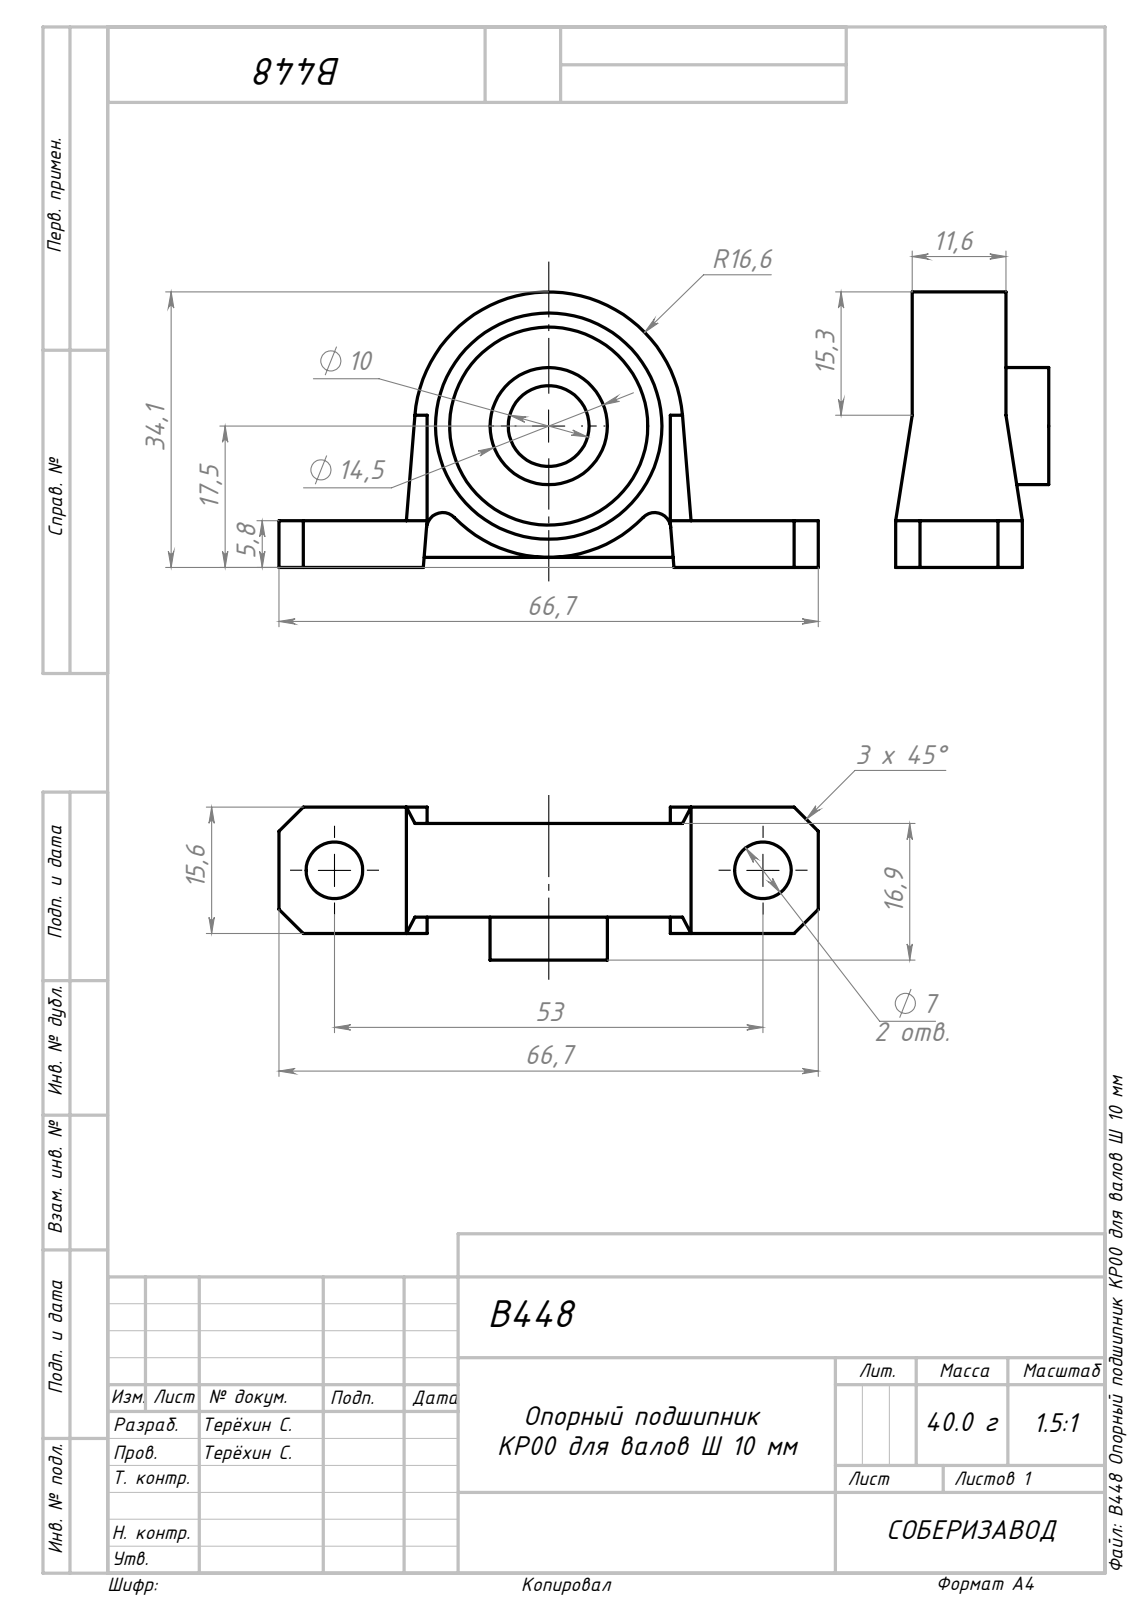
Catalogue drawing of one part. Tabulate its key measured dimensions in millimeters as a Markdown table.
| quantity | value |
| --- | --- |
| part name | B448 Опорный подшипник KP00 для валов Ø 10 мм_00; Сборка2 |
| STEP written by | SolidWorks 2024 (AUTOMOTIVE_DESIGN) |
| units | millimeters |
| bodies | 3 solids, 64 faces (39 planar, 25 cylindrical, 0 other) |
| overall size | 66.7 × 34.1 × 18.93 |
| volume | 11 584 mm³ |
| surface area | 8 004 mm² |
| round holes (diameter × count) | 7 × 2, 10 × 1, 14.5 × 1, 24.5 × 1, 28 × 1 |
| partial cylindrical surfaces (radius × count) | 2 × 2, 16.25 × 1, 16.6 × 1 |
| main face-to-face distances | 1.8, 9.8, 5.8, 8, 4, 11.65, 1.25, 4.55, 11.6, 2.02 |
| hole center spacings | 53 |
